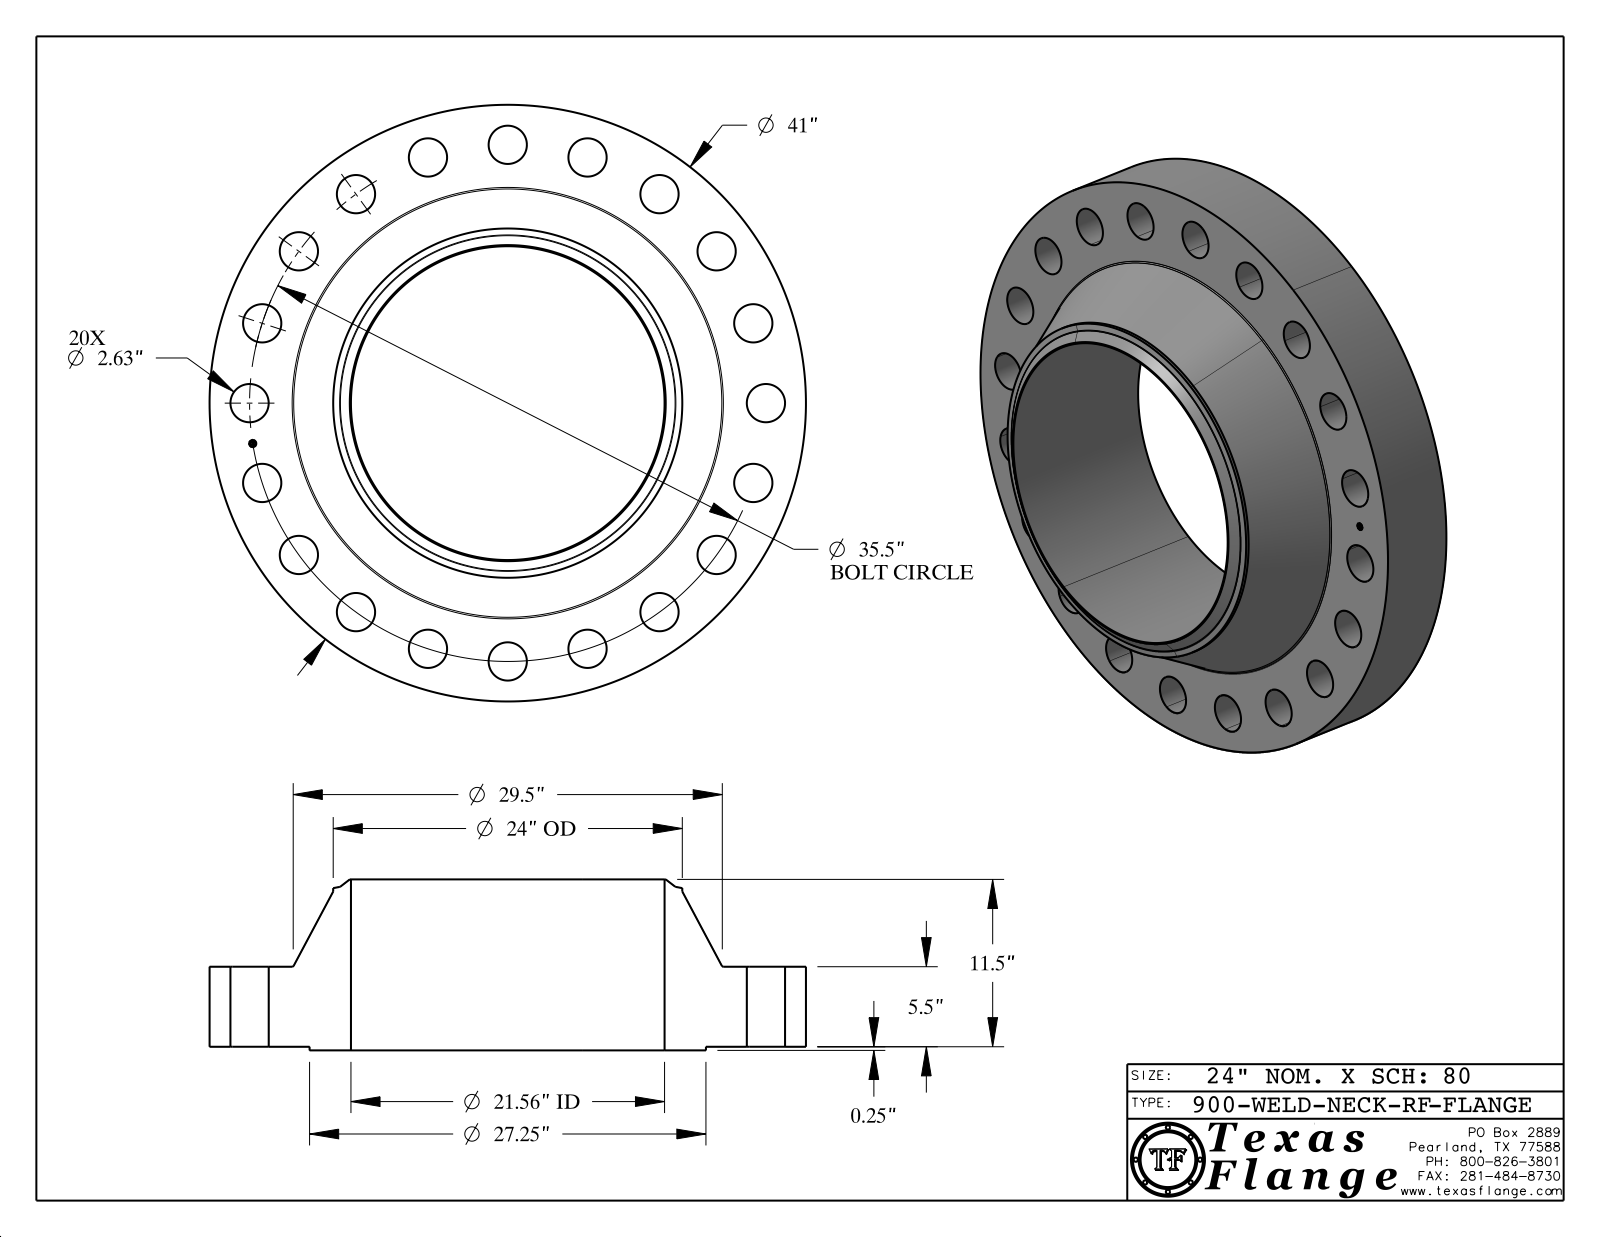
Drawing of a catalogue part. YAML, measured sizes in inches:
part_name: "900-WELD-NECK-RF"
step_written_by: "CATIA V5 STEP AP214 (AUTOMOTIVE_DESIGN)"
units: inches
bodies: {solids: 1, faces: 447, planar: 369, cylindrical: 68, other: 10}
overall_size: [41, 41, 11.75]
volume: 5779
surface_area: 4418
round_holes:
  - {diameter: 2.63, count: 20}
  - {diameter: 0.495, count: 1}
  - {diameter: 21.562, count: 1}
round_bosses_or_shafts:
  - {diameter: 0.03, count: 8}
  - {diameter: 41, count: 1}
  - {diameter: 27.25, count: 1}
  - {diameter: 24, count: 1}
  - {diameter: 0.39, count: 1}
face_to_face_distances: [5.5, 0.25, 5.75, 11.75, 11.5, 6, 5.735, 5.485, 0.015, 6.015]
hole_center_spacings: [17.75, 10.97, 28.72, 31.631, 16.117, 20.866, 25.102, 33.762]
